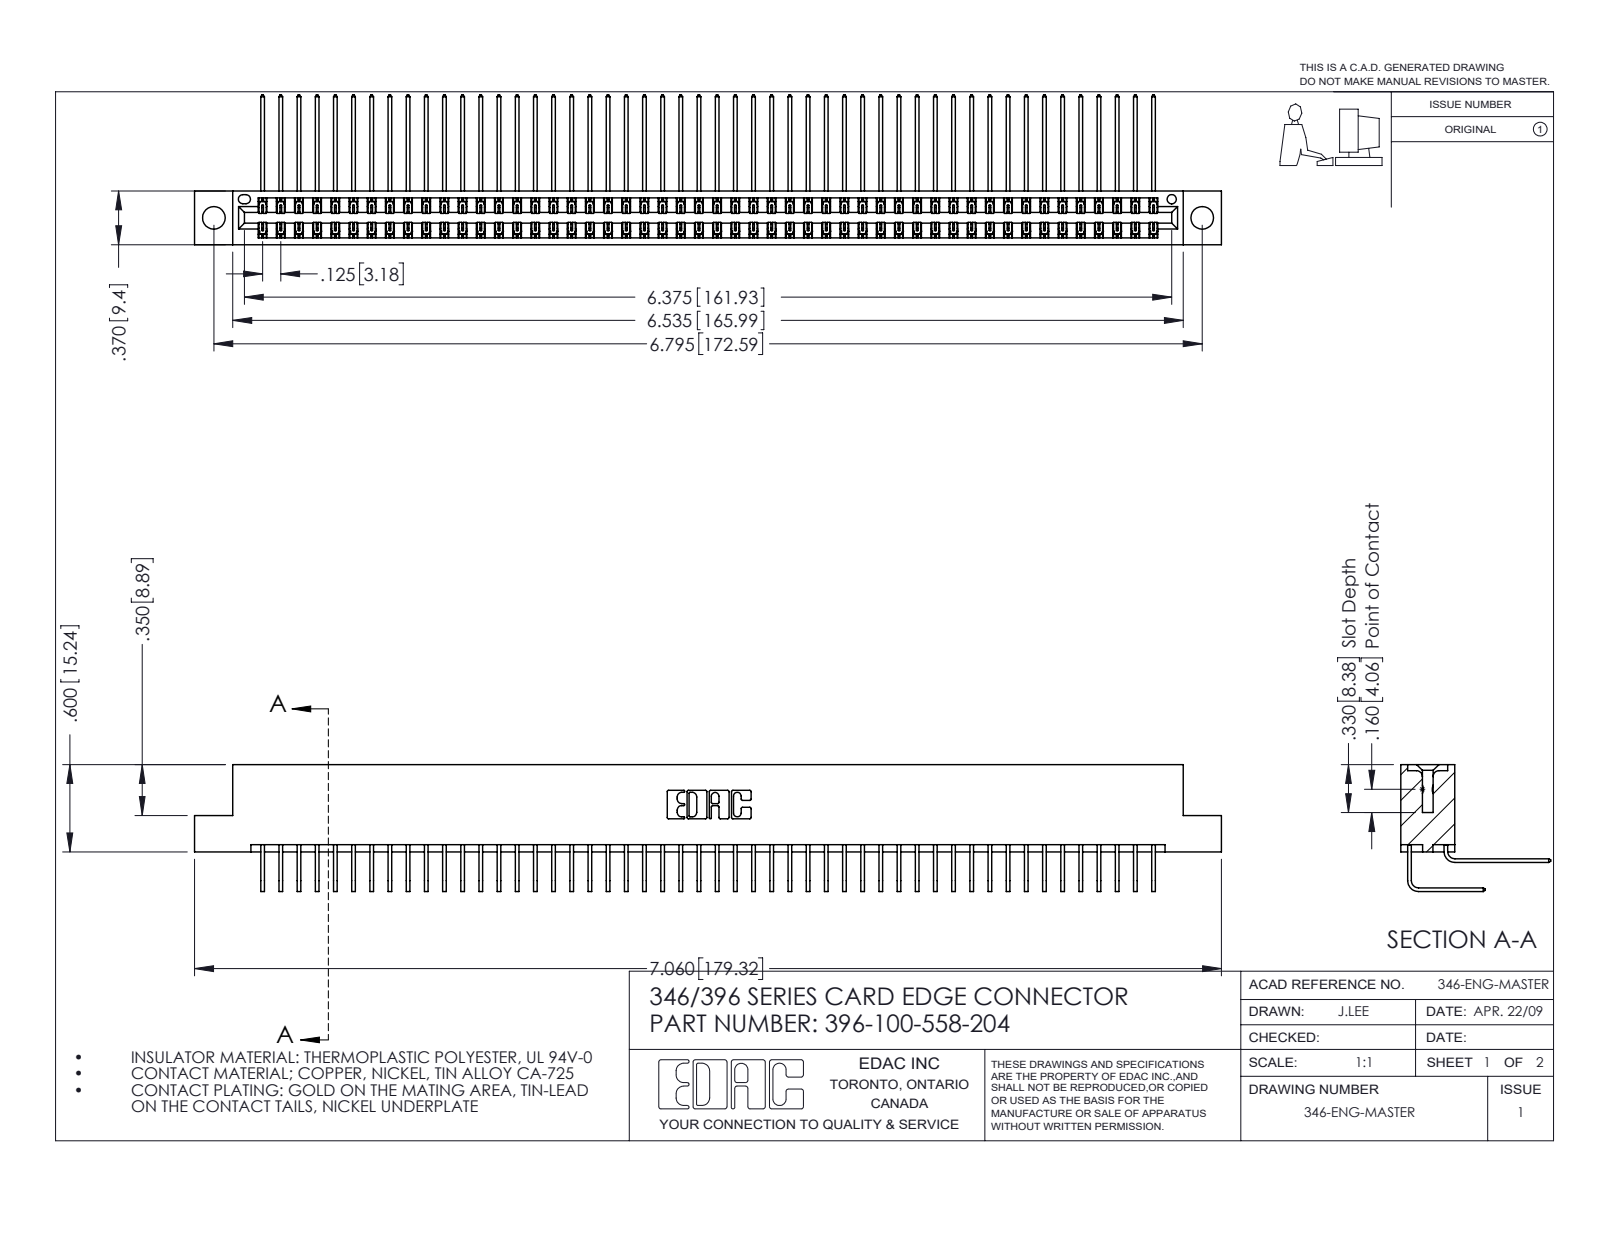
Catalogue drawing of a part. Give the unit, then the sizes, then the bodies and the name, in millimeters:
Units: millimetres
Overall size (bounding box): 179.3 × 26.2 × 22.2
Round holes (diameter × count): ⌀4 ×2, ⌀1.6 ×1
Partial cylindrical surfaces — rounded edges, fillets, slot ends (radius × count): R0.2 ×150, R0.3 ×22, R0.2 ×6, R0.8 ×6, R0.7 ×3, R0.4 ×2, R0.6 ×2, R0.6 ×2
Main face-to-face distances: 8.2, 1.2, 0.6, 9.4, 6.4, 7.6, 1.8, 7, 3.8, 5.6
Hole centre spacings: 6.2, 167.3, 172.6
Volume: 18 040 mm³ · Surface area: 27 500 mm²
Bodies: 101 solids, 5522 faces (3776 planar, 1746 cylindrical, 0 other)
Part name (STEP PRODUCT): 396-100-558-204; 345-292-001_558 559 Tail - 1; 345-292-001_558 Tail - 2; 346 Part_Flush Mounting Lugs - 0.156 Dia-TH
STEP written by: SolidWorks 2016 (CONFIG_CONTROL_DESIGN)
